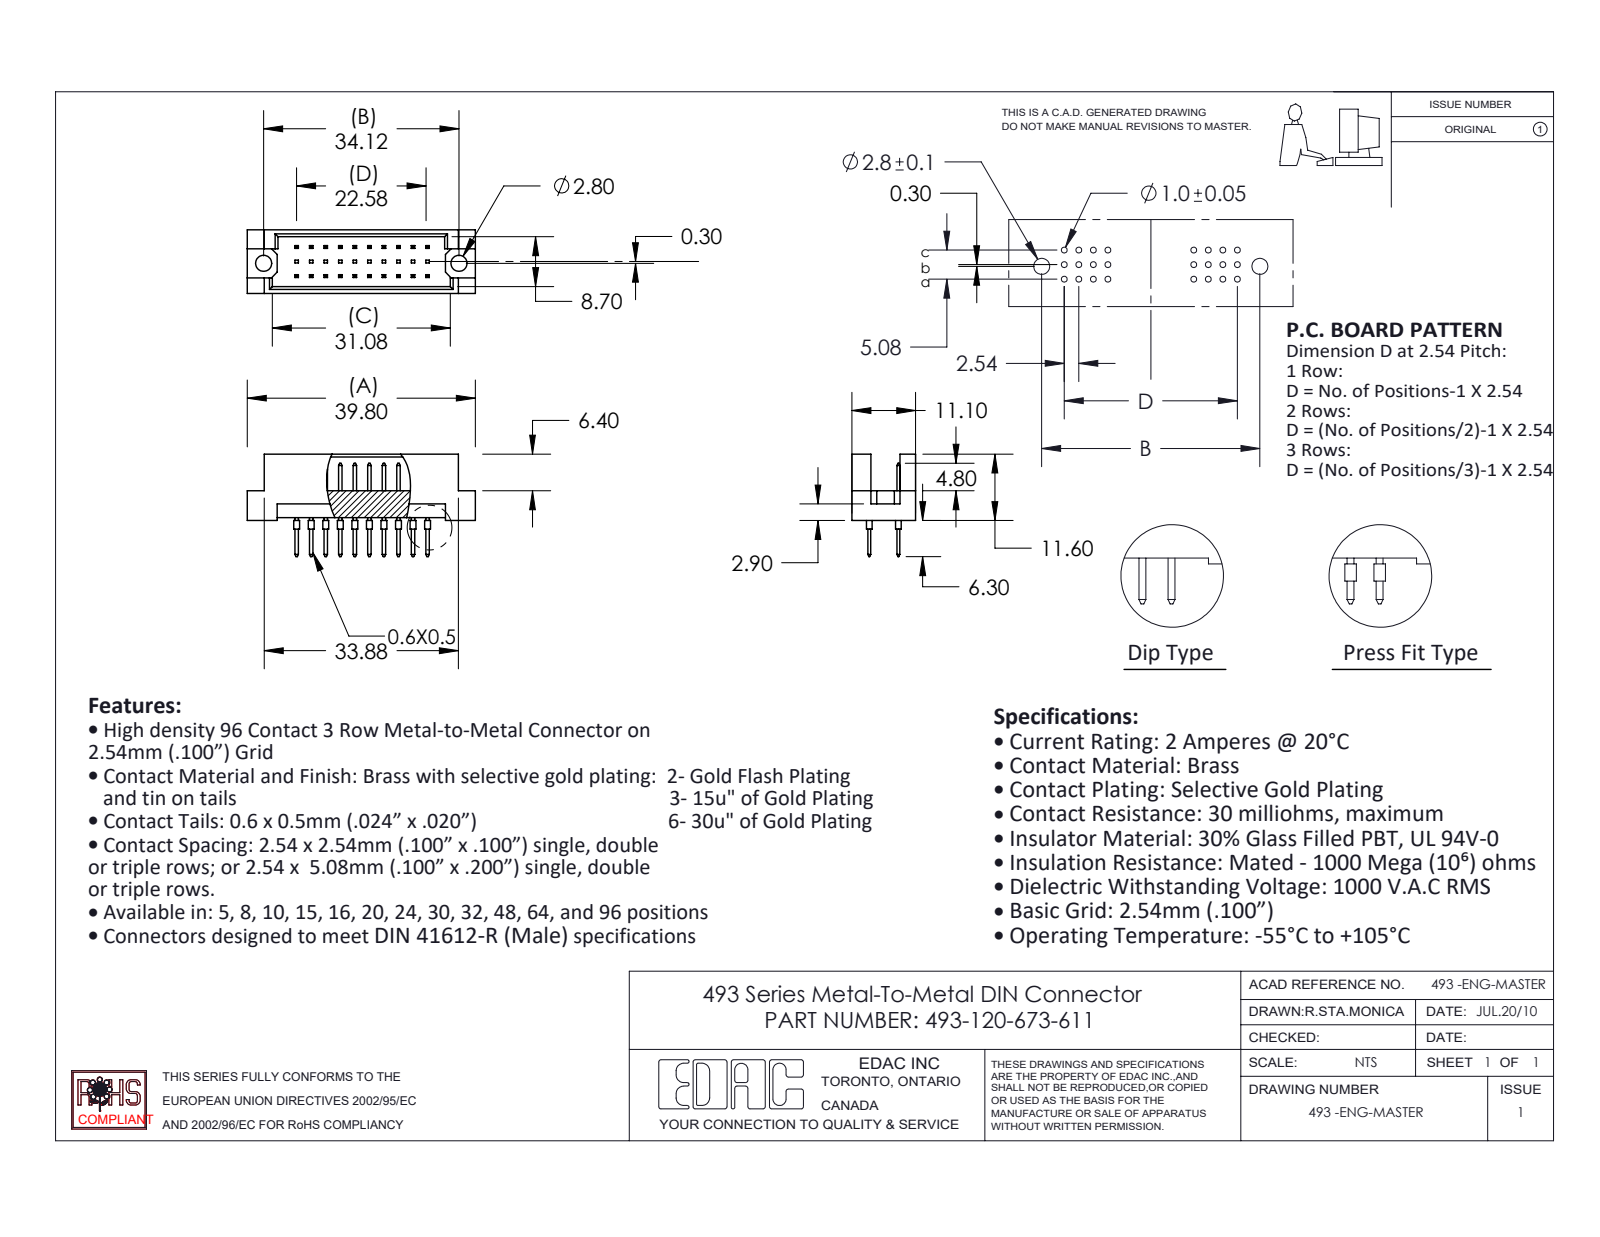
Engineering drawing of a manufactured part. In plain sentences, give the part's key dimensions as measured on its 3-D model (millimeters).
The part is named "493-290_73; 493-120-673-611; 493 Part_30". Its 3-D file was written by "SolidWorks 2020 (CONFIG_CONTROL_DESIGN)". It is 21 solids with 612 faces: 568 planar, 44 cylindrical and 0 other. Overall it measures 39.8 by 17.9 by 11.1 millimeters. Its volume is 2 483 cubic millimeters and its surface area 3 495 square millimeters. Round holes: 2 of diameter 2.8. Round bosses or shafts: 20 of diameter 1. The main face-to-face distances are 5.08, 1.2, 9.9, 2.54, 11.1, 0.5, 8.7, 4.7, 2.76, 3.26. The hole center spacings are 34.12.
